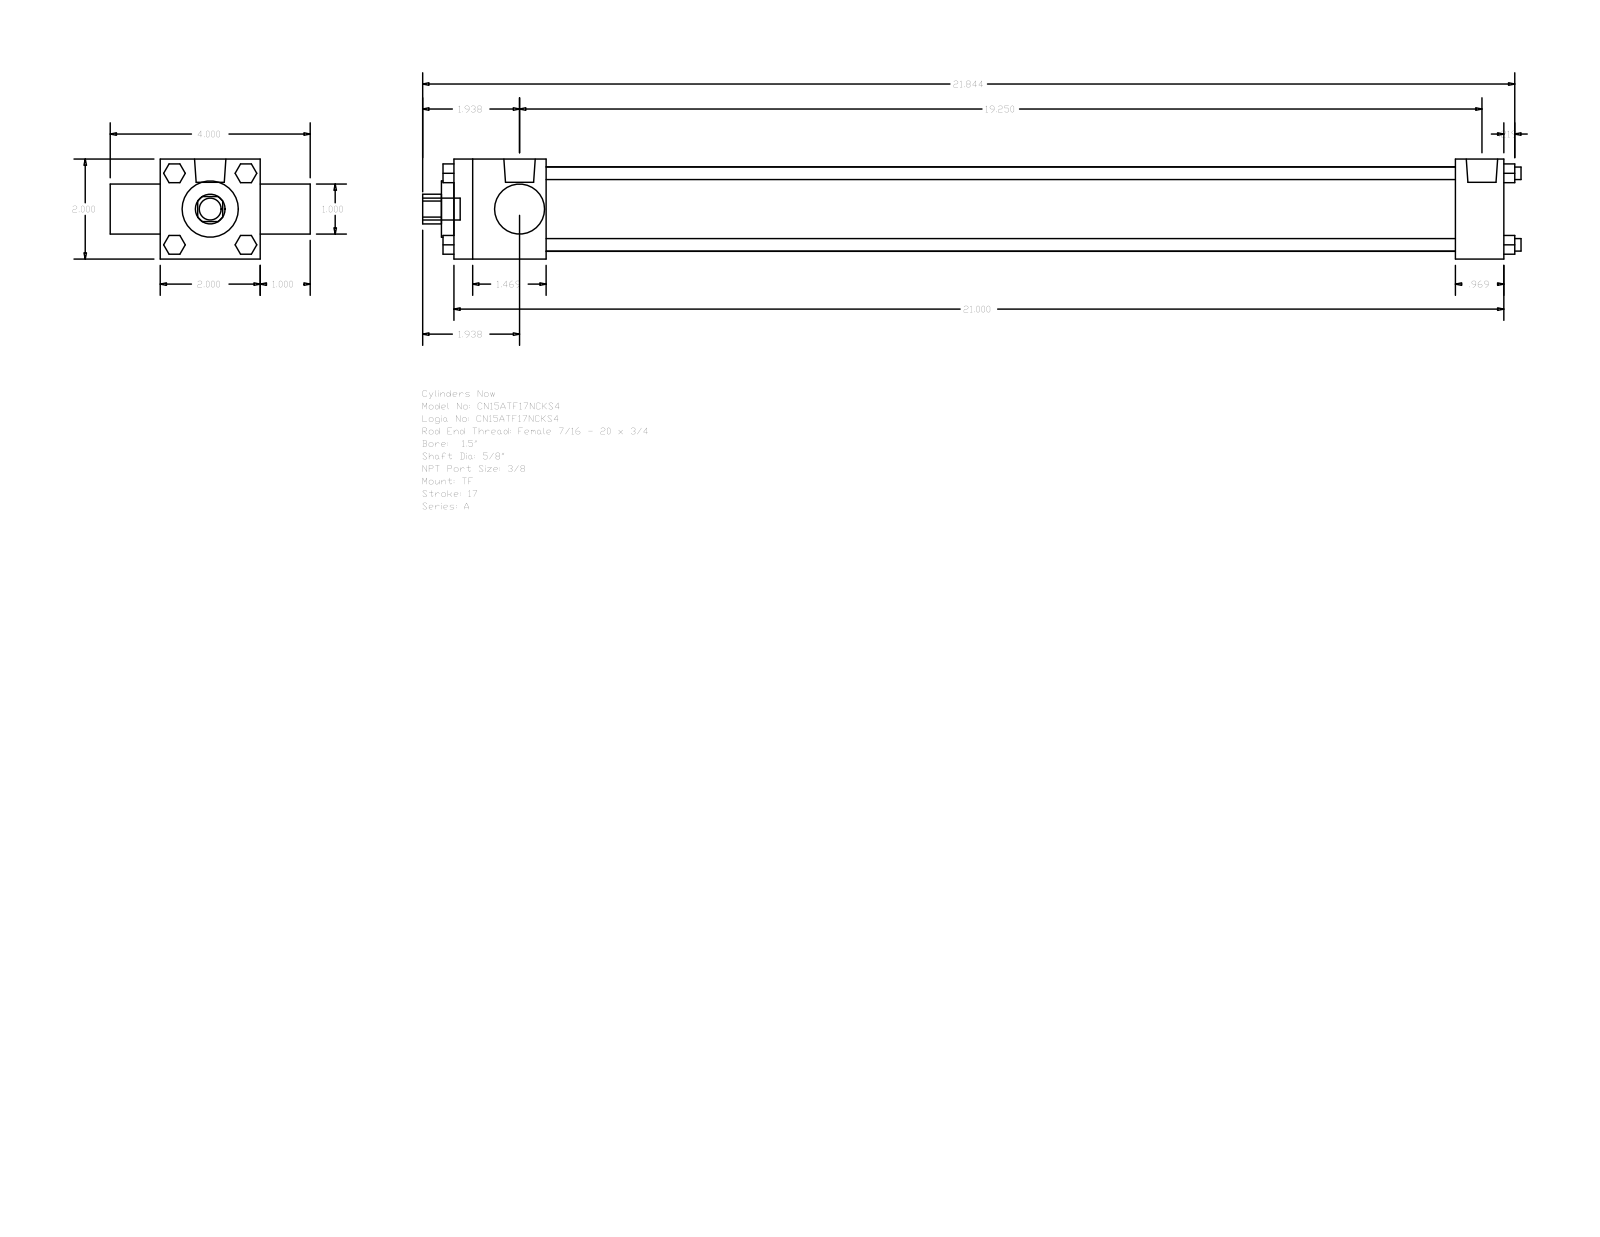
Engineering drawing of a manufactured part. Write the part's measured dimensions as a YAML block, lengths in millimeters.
part_name: "A_TF__0150_0.625"
step_written_by: "GSSL Pune (CONFIG_CONTROL_DESIGN)"
units: millimeters
bodies: {solids: 0, faces: 120, planar: 92, cylindrical: 28, other: 0}
overall_size: [558.01, 101.6, 50.8]
round_holes:
  - {diameter: 15.88, count: 1}
  - {diameter: 25.4, count: 1}
  - {diameter: 28.57, count: 1}
  - {diameter: 42.93, count: 1}
round_bosses_or_shafts:
  - {diameter: 6.35, count: 4}
  - {diameter: 5.56, count: 3}
  - {diameter: 15.93, count: 2}
  - {diameter: 11.11, count: 1}
partial_cylinders:
  - {radius: 7.54, count: 1}
face_to_face_distances: [50.8, 533.39, 25.4, 76.2, 46.83, 508.79, 461.96, 486.56, 24.6, 9.52]
